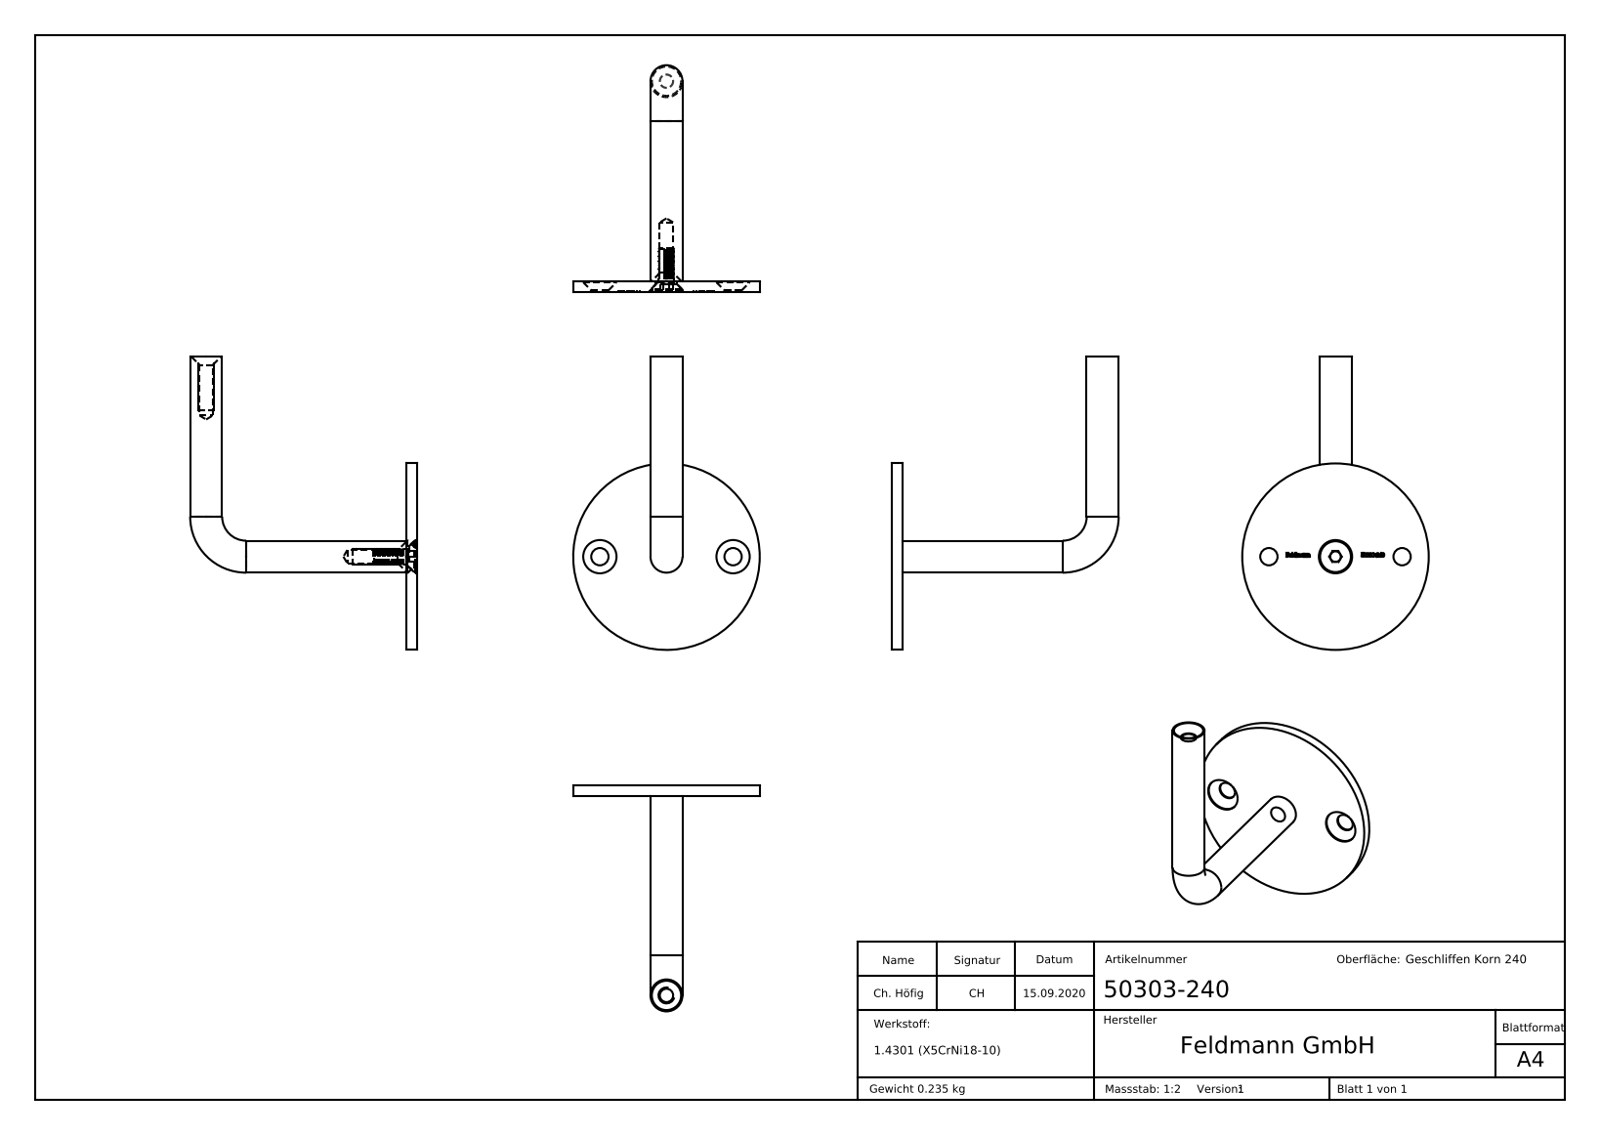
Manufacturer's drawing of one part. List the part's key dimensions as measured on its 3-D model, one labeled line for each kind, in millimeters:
Part name (STEP PRODUCT): 50303-240; socket countersunk head screw_din_DIN 7991 - M6 x 16 --- 16S; socket countersunk head screw_din; 50303-240 Teil2_50303-240 Teil 2 (+3 more)
STEP written by: SolidWorks 2018 (CONFIG_CONTROL_DESIGN)
Units: millimetres
Bodies: 3 solids, 368 faces (131 planar, 48 cylindrical, 189 other)
Overall size (bounding box): 110 × 85 × 70
Volume: 30 139 mm³ · Surface area: 15 505 mm²
Round holes (diameter × count): ⌀12.5 ×3, ⌀5 ×2, ⌀6.5 ×2, ⌀8 ×1
Round bosses / shafts (diameter × count): ⌀12 ×2, ⌀70 ×1, ⌀11.57 ×1, ⌀6 ×1
Main face-to-face distances: 4, 3.55, 0.45, 16.45, 16, 12.45, 4.02, 0.35, 3.9, 16.35
Hole centre spacings: 25, 50
